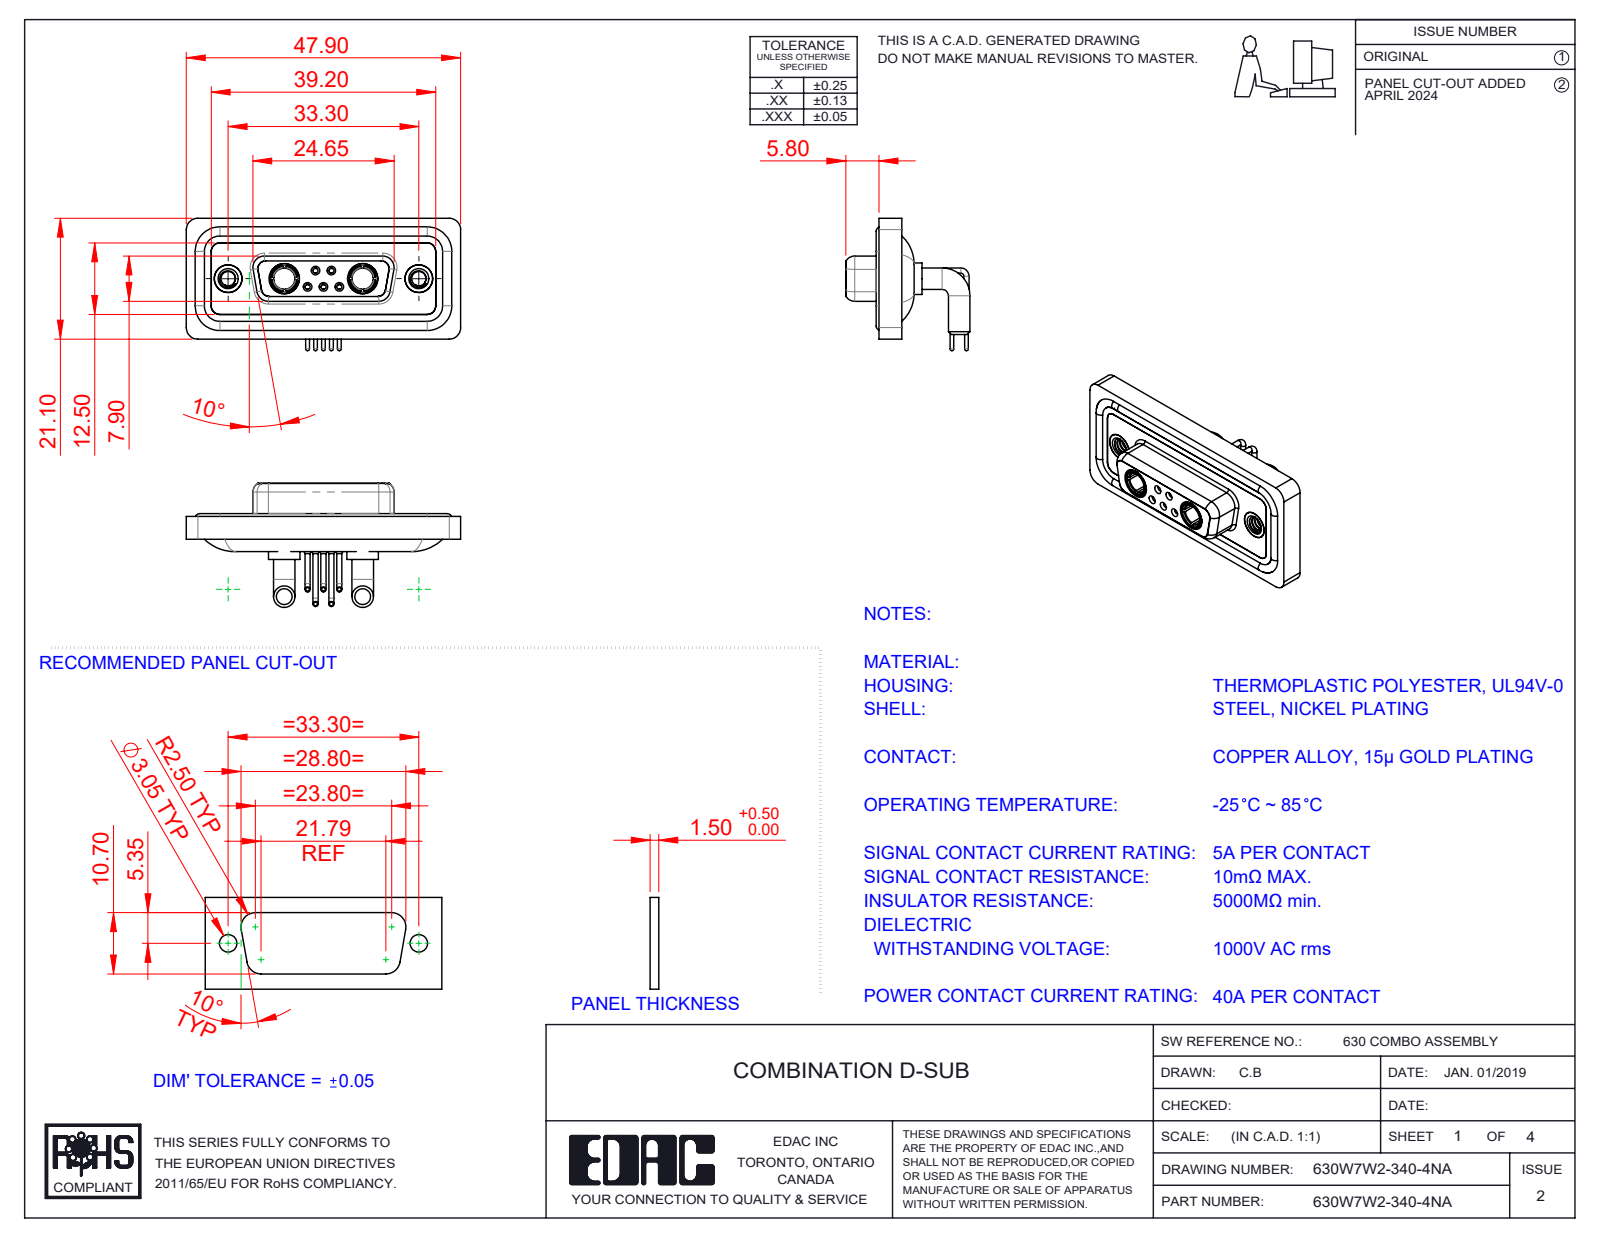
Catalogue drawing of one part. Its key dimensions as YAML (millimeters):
part_name: "630Combo Contact Row 1_50 Contacts; 630Combo Shell Front_15 Contacts; 630Combo Contact Row 2_50 Contacts; 630Combo Threaded Rivet_A (+5 more)"
step_written_by: "SolidWorks 2023 (CONFIG_CONTROL_DESIGN)"
units: millimeters
bodies: {solids: 16, faces: 801, planar: 238, cylindrical: 351, other: 212}
overall_size: [47.9, 23.12, 21.68]
volume: 6334
surface_area: 10296
round_holes:
  - {diameter: 0.9, count: 5}
  - {diameter: 1.1, count: 5}
  - {diameter: 1.5, count: 5}
  - {diameter: 2, count: 5}
  - {diameter: 4.85, count: 4}
  - {diameter: 1.6, count: 3}
  - {diameter: 1.7, count: 2}
  - {diameter: 2.5, count: 2}
  - {diameter: 3.7, count: 2}
  - {diameter: 4, count: 2}
  - {diameter: 4.05, count: 2}
  - {diameter: 5, count: 2}
round_bosses_or_shafts:
  - {diameter: 1.6, count: 6}
  - {diameter: 0.9, count: 5}
  - {diameter: 0.65, count: 5}
  - {diameter: 3.75, count: 4}
  - {diameter: 5.5, count: 2}
  - {diameter: 5.2, count: 2}
  - {diameter: 4.96, count: 2}
  - {diameter: 4.95, count: 2}
partial_cylinders:
  - {radius: 2, count: 20}
  - {radius: 1.5, count: 18}
  - {radius: 1.35, count: 12}
  - {radius: 1.6, count: 8}
  - {radius: 0.25, count: 4}
  - {radius: 0.5, count: 4}
  - {radius: 0.6, count: 4}
  - {radius: 0.65, count: 4}
face_to_face_distances: [0.4, 1.8, 1.1, 1.6, 2.9, 2.5, 3.1, 3.7, 4.1, 1.5]
hole_center_spacings: [3.16, 2.77, 9.8, 23.5, 4.31, 4.33, 5.03, 5.04]
